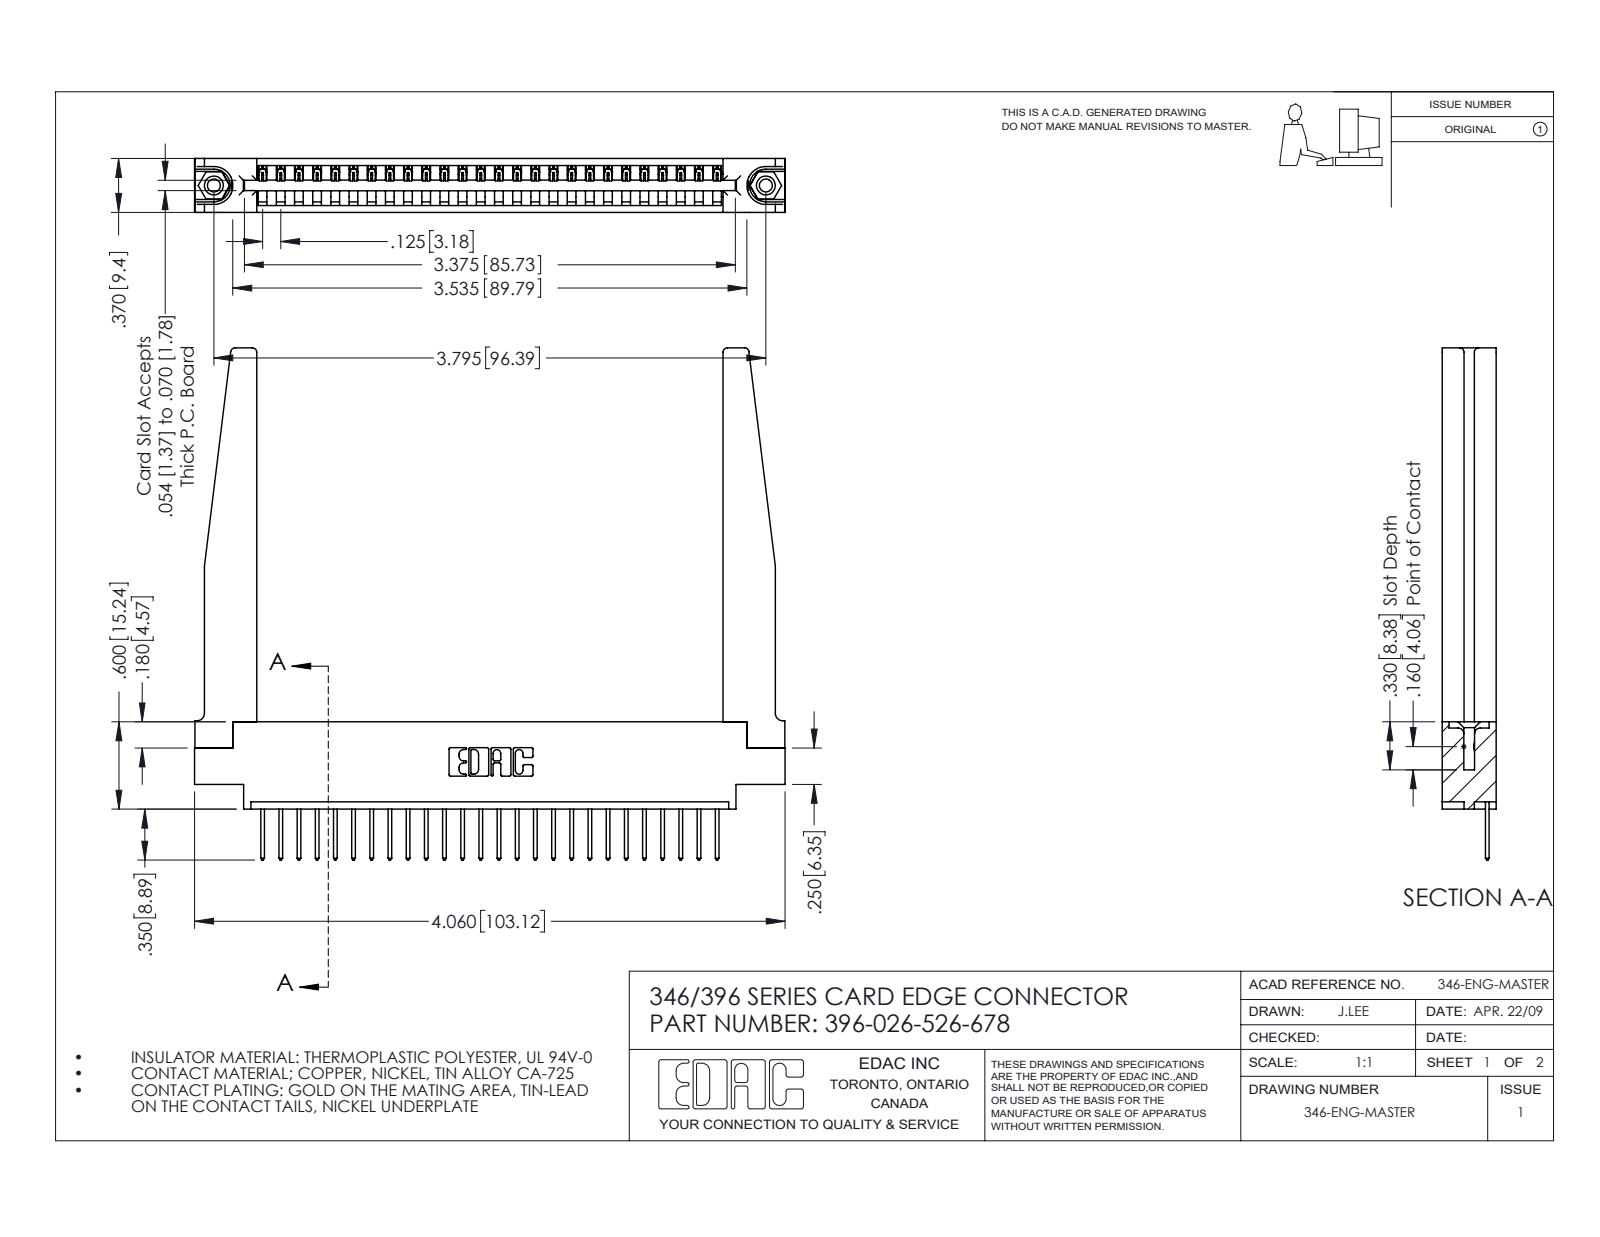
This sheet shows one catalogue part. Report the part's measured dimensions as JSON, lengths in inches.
{"part_name": "346 Part_0.170 Offset - 0.156 Dia-TH; 345-250-001_345-250-001-102; 346-220-078_345-220-078; 396-026-526-678 (+1 more)", "step_written_by": "SolidWorks 2016 (CONFIG_CONTROL_DESIGN)", "units": "inches", "bodies": {"solids": 31, "faces": 1868, "planar": 1262, "cylindrical": 554, "other": 52}, "overall_size": [4.06, 3.52, 0.37], "volume_in3": 1.007, "surface_area_in2": 28.65, "round_holes": [[0.089, 2], [0.125, 2], [0.156, 2], [0.064, 1]], "round_bosses_or_shafts": [[0.155, 2]], "partial_cylinders_radius": [[0.006, 52], [0.01, 52], [0.01, 22], [0.03, 8], [0.007, 6], [0.031, 6], [0.026, 3], [0.031, 2]], "face_to_face_distances": [0.37, 0.048, 0.322, 0.072, 0.148, 0.15, 0.25, 0.298, 0.025, 0.222], "hole_center_spacings": [0.246, 3.587, 3.795]}
